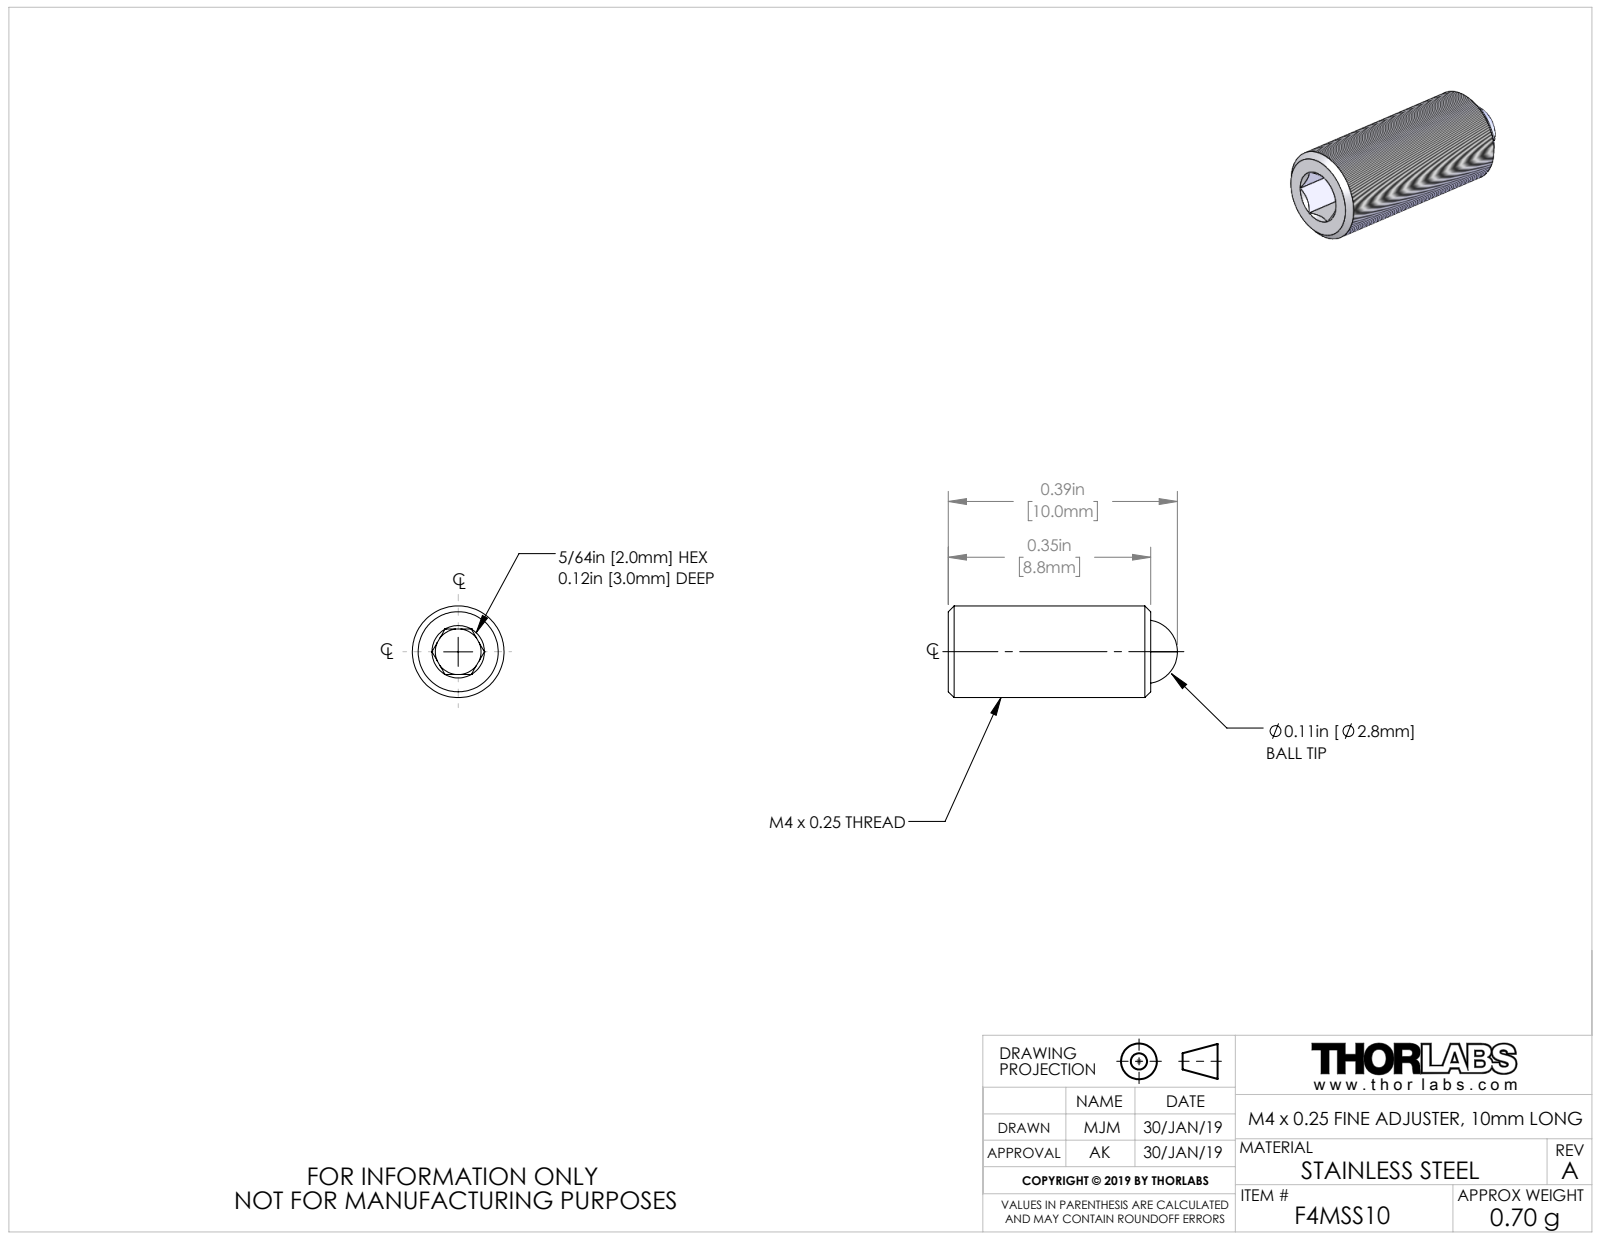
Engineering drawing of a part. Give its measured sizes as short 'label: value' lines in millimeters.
name: TTN174696-E0W
written by: SolidWorks 2018 (AUTOMOTIVE_DESIGN)
unit: mm
bodies: 2 solids, 45 faces (20 planar, 6 cylindrical, 19 other)
size: 10 × 4 × 4
volume: 100 mm³; area: 193 mm²
holes: 1× ⌀2, 1× ⌀2.8
bosses: 1× ⌀4
face distances: 2, 8.8, 5.8, 3
